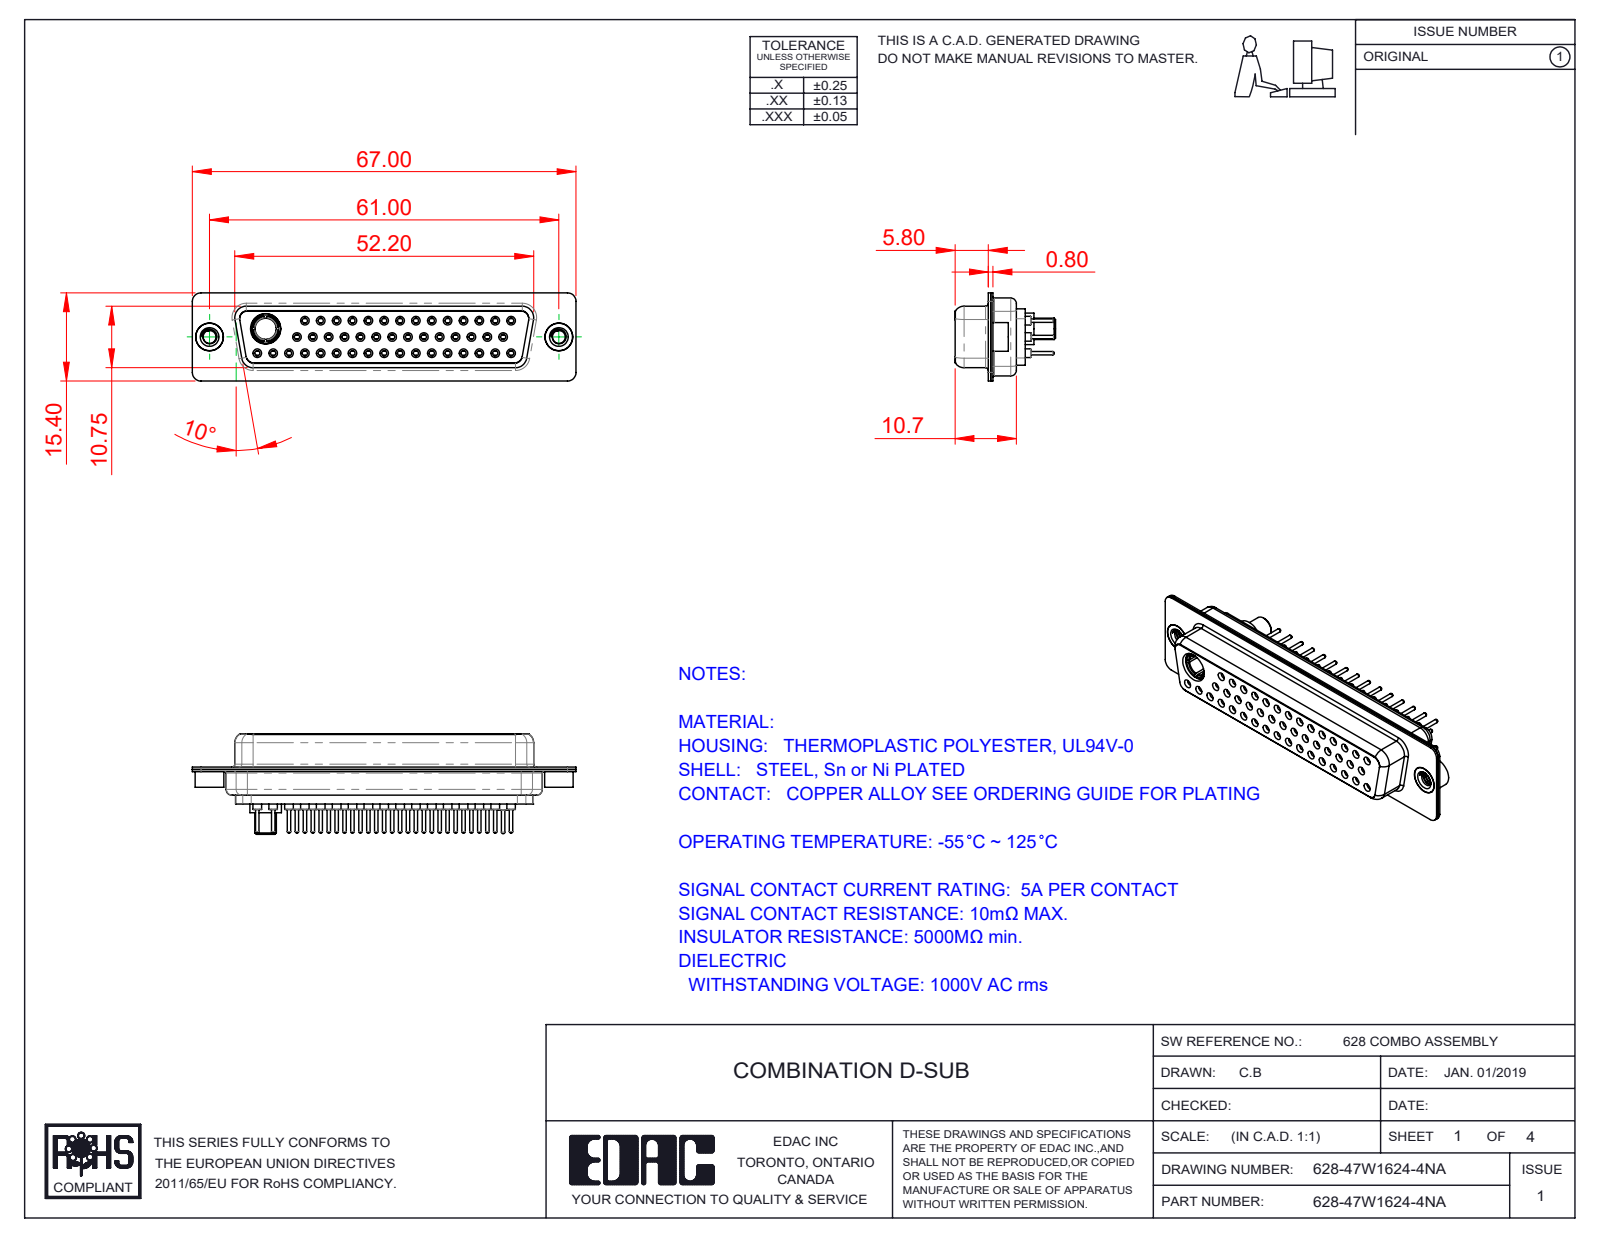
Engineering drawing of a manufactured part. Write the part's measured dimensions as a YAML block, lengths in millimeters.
part_name: "628Combo Contact Row 3_24; 628-47W1624-4NA; Power Socket_40A S; 628Combo Shell Front_50 Contacts (+5 more)"
step_written_by: "SolidWorks 2016 (CONFIG_CONTROL_DESIGN)"
units: millimeters
bodies: {solids: 53, faces: 2869, planar: 783, cylindrical: 1028, other: 1058}
overall_size: [67, 17.55, 15.4]
volume: 7106
surface_area: 14699
round_holes:
  - {diameter: 1.1, count: 46}
  - {diameter: 0.9, count: 45}
  - {diameter: 1.5, count: 45}
  - {diameter: 2, count: 45}
  - {diameter: 1.6, count: 31}
  - {diameter: 1.7, count: 14}
  - {diameter: 4.85, count: 3}
  - {diameter: 2.26, count: 2}
  - {diameter: 4, count: 2}
  - {diameter: 4.05, count: 2}
  - {diameter: 3.7, count: 1}
  - {diameter: 5.3, count: 1}
round_bosses_or_shafts:
  - {diameter: 2.2, count: 46}
  - {diameter: 0.6, count: 46}
  - {diameter: 1.6, count: 15}
  - {diameter: 5, count: 2}
  - {diameter: 4.95, count: 2}
  - {diameter: 4.8, count: 2}
  - {diameter: 5.5, count: 1}
  - {diameter: 5.2, count: 1}
partial_cylinders:
  - {radius: 1.5, count: 16}
  - {radius: 1.35, count: 12}
  - {radius: 2, count: 12}
  - {radius: 1.6, count: 8}
  - {radius: 0.25, count: 4}
  - {radius: 0.5, count: 4}
  - {radius: 0.6, count: 4}
  - {radius: 0.65, count: 4}
face_to_face_distances: [0.4, 11.33, 6.45, 6.05, 1.87, 12.25, 6.2, 5.8, 10.35, 10.93]
hole_center_spacings: [3.16, 2.77, 5.54, 8.31, 11.08, 13.85, 16.62, 19.39]
